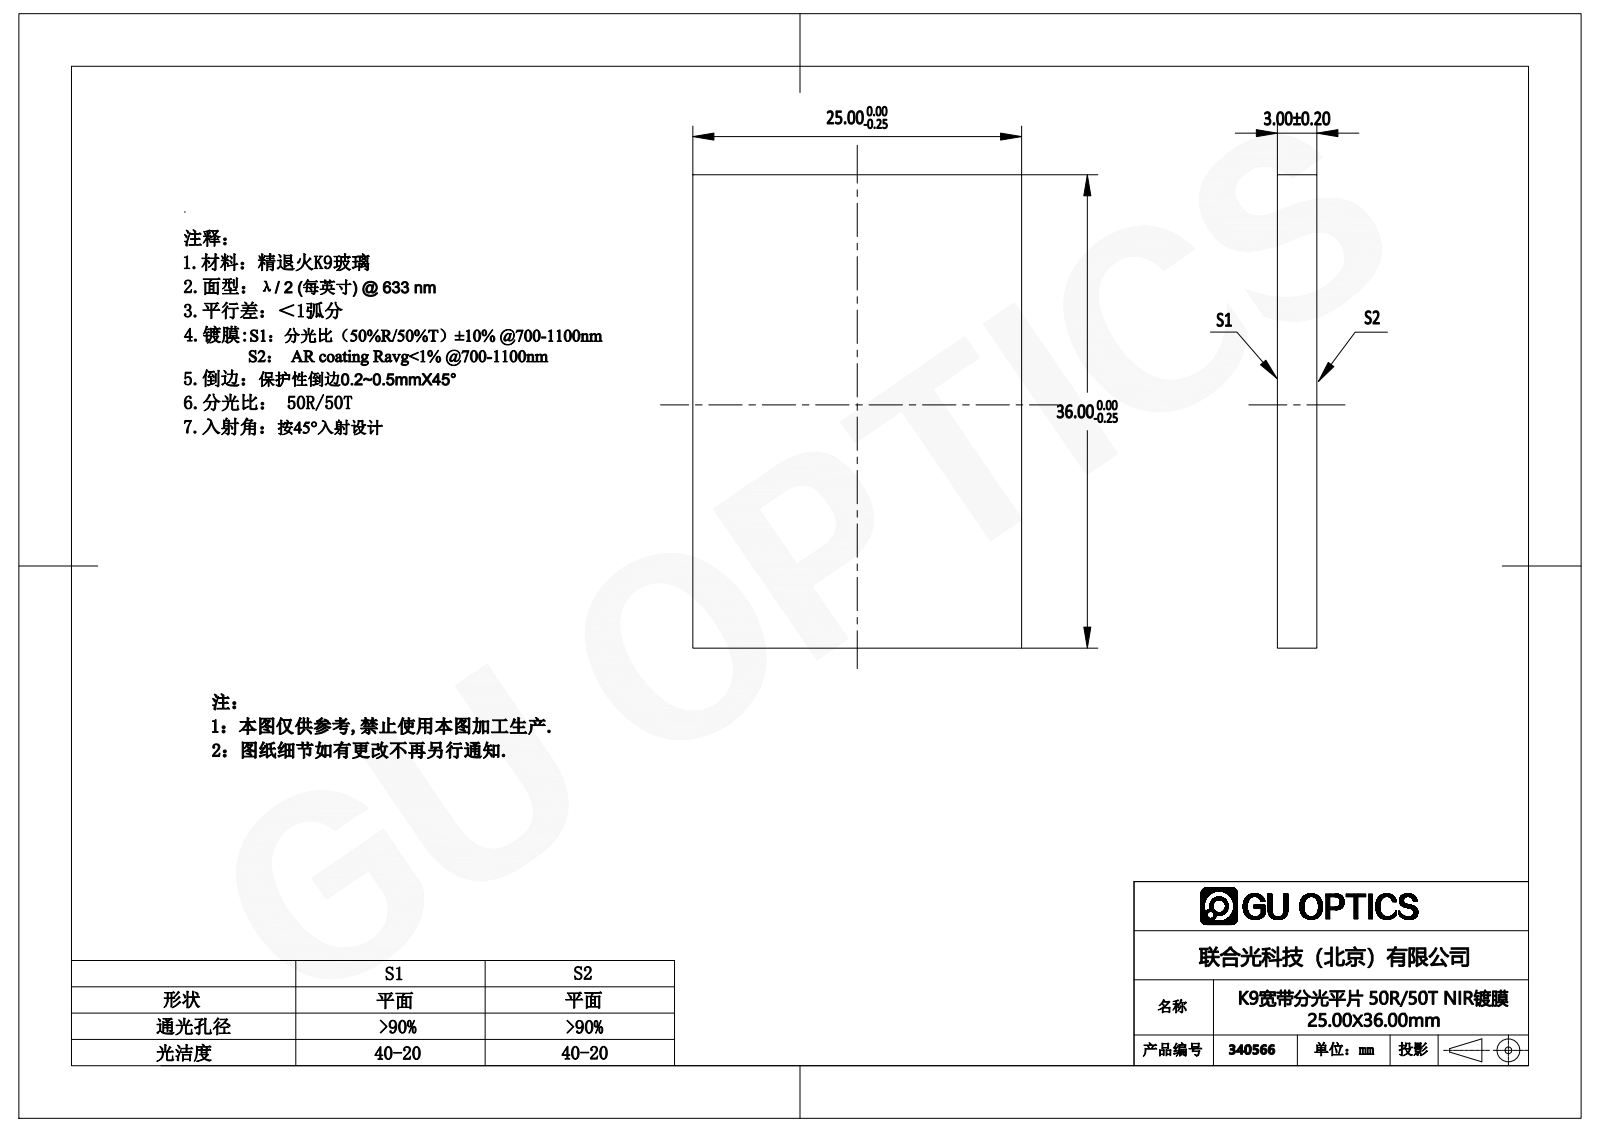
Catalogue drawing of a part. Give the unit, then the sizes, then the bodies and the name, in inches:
Units: inches
Overall size (bounding box): 1.417 × 0.984 × 0.118
Main face-to-face distances: 0.118, 0.984, 1.417
Volume: 0.165 in³ · Surface area: 3.357 in²
Bodies: 1 solid, 6 faces (6 planar, 0 cylindrical, 0 other)
Part name (STEP PRODUCT): 340524
STEP written by: SolidWorks 2016 (CONFIG_CONTROL_DESIGN)
